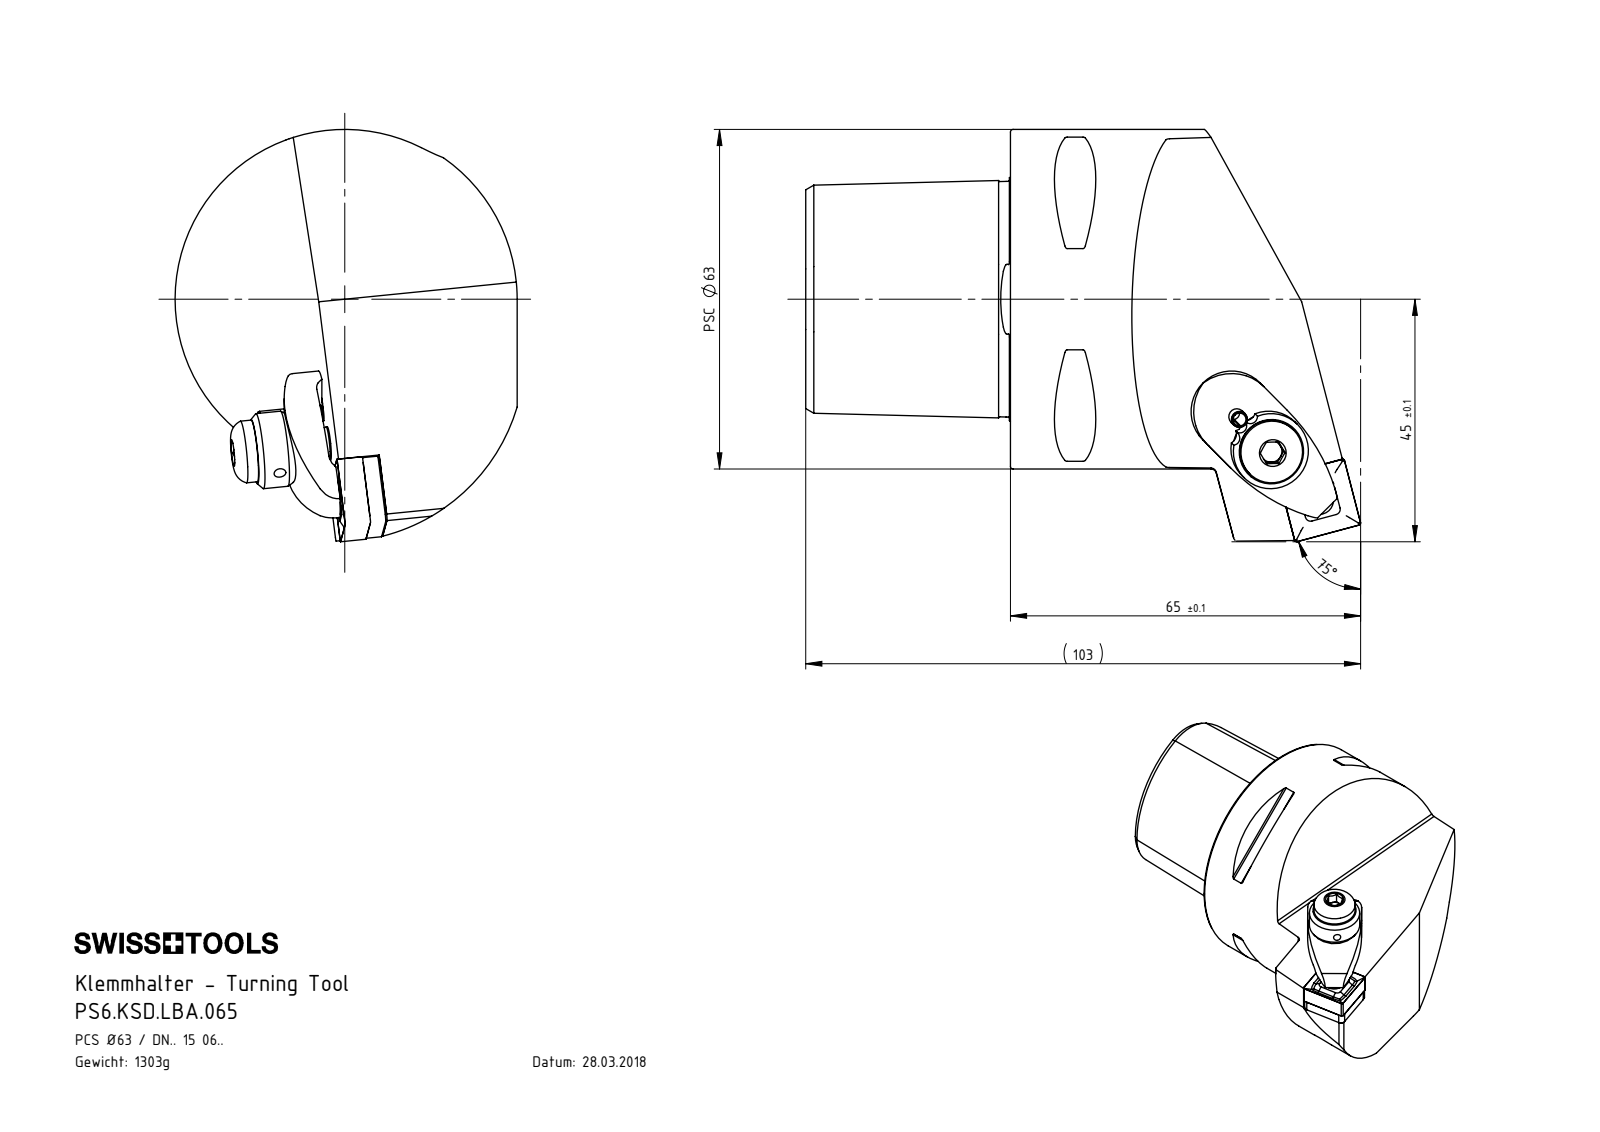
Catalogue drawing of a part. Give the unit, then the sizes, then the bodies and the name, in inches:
Units: inches
Overall size (bounding box): 4.055 × 3.012 × 2.5
Round holes (diameter × count): ⌀0.079 ×3, ⌀0.197 ×3, ⌀0.165 ×2, ⌀0.244 ×2, ⌀0.276 ×2, ⌀0.094 ×1, ⌀0.118 ×1, ⌀0.157 ×1, ⌀0.203 ×1, ⌀0.236 ×1, ⌀0.256 ×1, ⌀0.319 ×1
Round bosses / shafts (diameter × count): ⌀0.236 ×2, ⌀0.118 ×2, ⌀2.48 ×1, ⌀0.551 ×1, ⌀0.453 ×1, ⌀0.276 ×1, ⌀0.268 ×1, ⌀0.244 ×1
Partial cylindrical surfaces — rounded edges, fillets, slot ends (radius × count): R0.02 ×8, R0.015 ×6, R0.027 ×6, R0.016 ×4, R0.031 ×3, R0.059 ×3, R0.079 ×2, R0.118 ×2
Main face-to-face distances: 1.496, 0.488, 0.98, 1.063, 0.433, 0.125, 0.3, 0.176, 0.352, 0.052
Hole centre spacings: 0.591, 0.906, 0.583, 0.298, 0.305, 0.313, 0.315, 0.323
Volume: 10.17 in³ · Surface area: 52.36 in²
Bodies: 11 solids, 433 faces (104 planar, 132 cylindrical, 197 other)
Part name (STEP PRODUCT): PS6.KSD.LBA.065; WSD-ER2.101.003_A; KVT_MB_600_060; SNMG120404 (+6 more)
STEP written by: SolidWorks 2022 (CONFIG_CONTROL_DESIGN)
